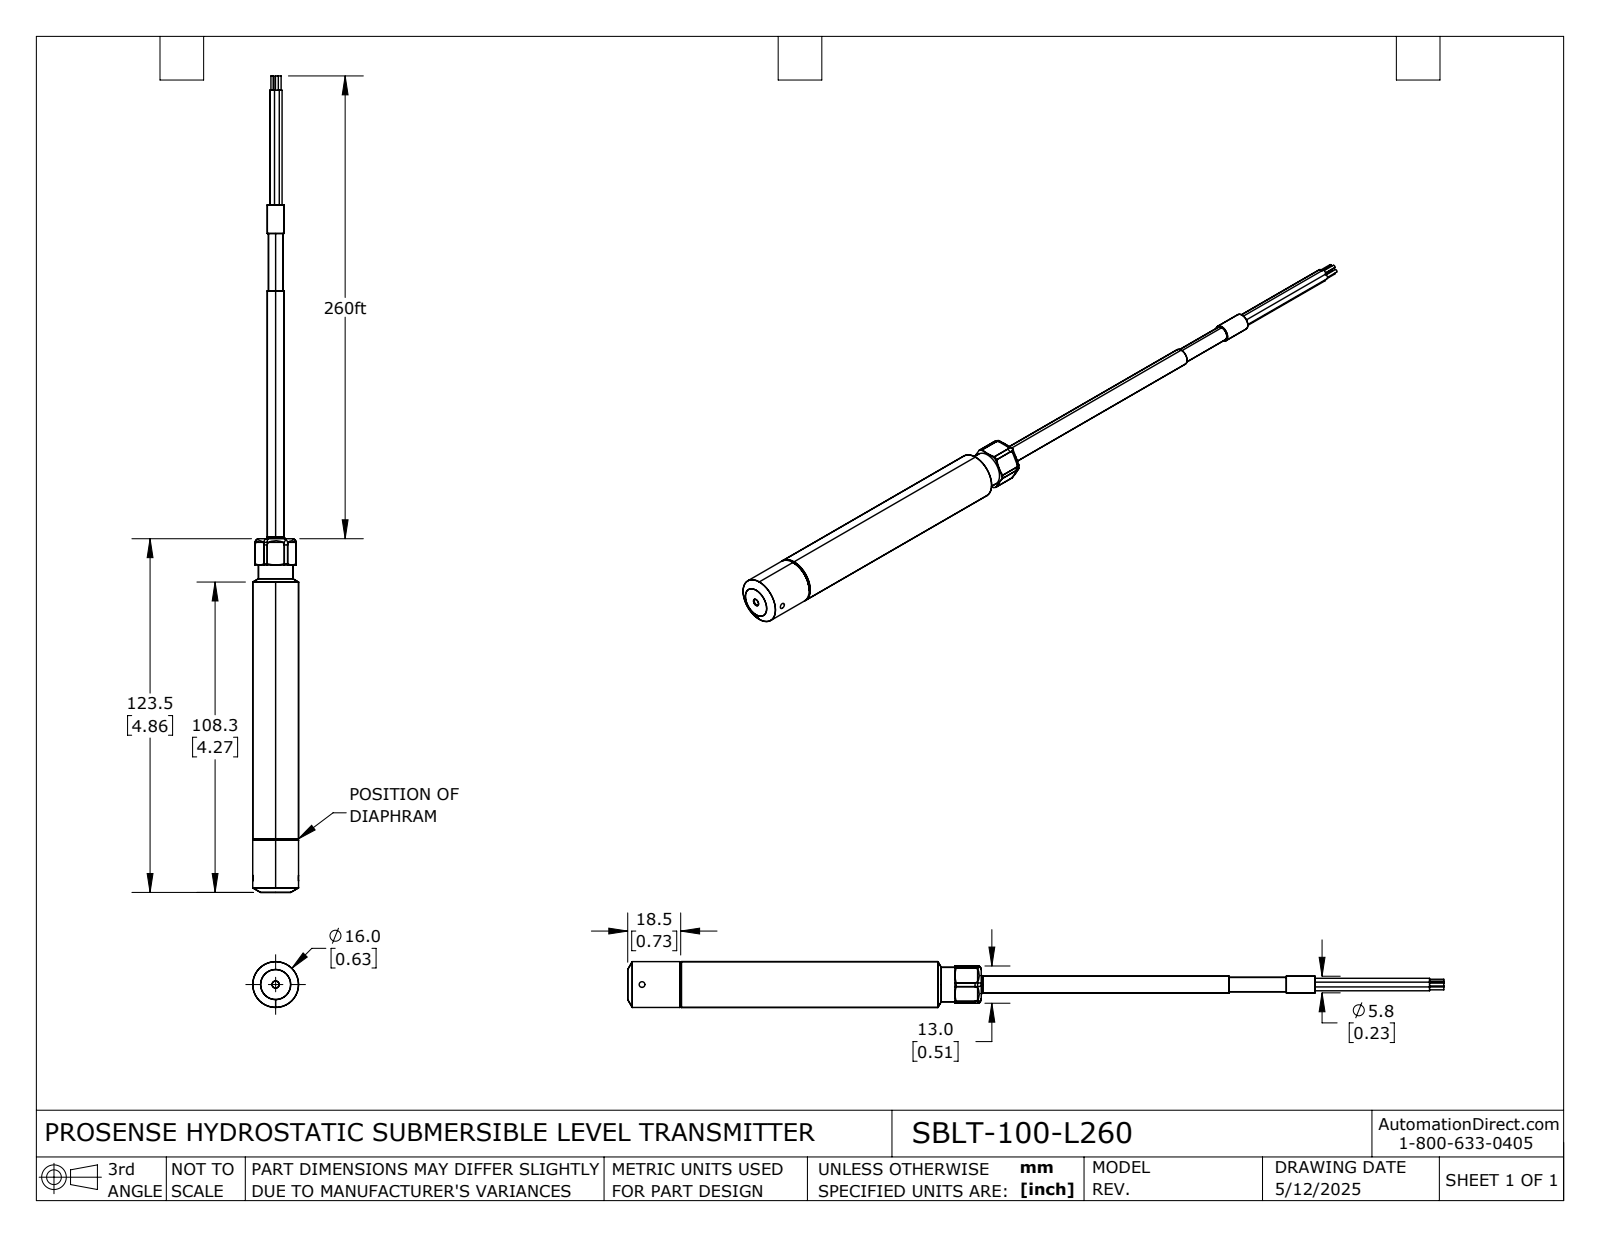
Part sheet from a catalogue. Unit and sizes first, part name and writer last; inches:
Units: inches
Overall size (bounding box): 11.221 × 0.63 × 0.63
Round holes (diameter × count): ⌀0.079 ×1, ⌀0.098 ×1, ⌀0.374 ×1, ⌀0.516 ×1, ⌀0.551 ×1
Round bosses / shafts (diameter × count): ⌀0.066 ×5, ⌀0.039 ×5, ⌀0.63 ×1, ⌀0.629 ×1, ⌀0.472 ×1, ⌀0.472 ×1, ⌀0.244 ×1, ⌀0.228 ×1
Partial cylindrical surfaces — rounded edges, fillets, slot ends (radius × count): R0.05 ×6, R0.281 ×1
Main face-to-face distances: 0.512, 4.861, 4.33, 0.531, 4.589, 8.918, 9.45, 3.77, 0.197, 8.721
Volume: 3.198 in³ · Surface area: 29.94 in²
Bodies: 11 solids, 201 faces (52 planar, 88 cylindrical, 61 other)
Part name (STEP PRODUCT): SBLT-100-L260
STEP written by: SolidWorks 2024 (AUTOMOTIVE_DESIGN)
